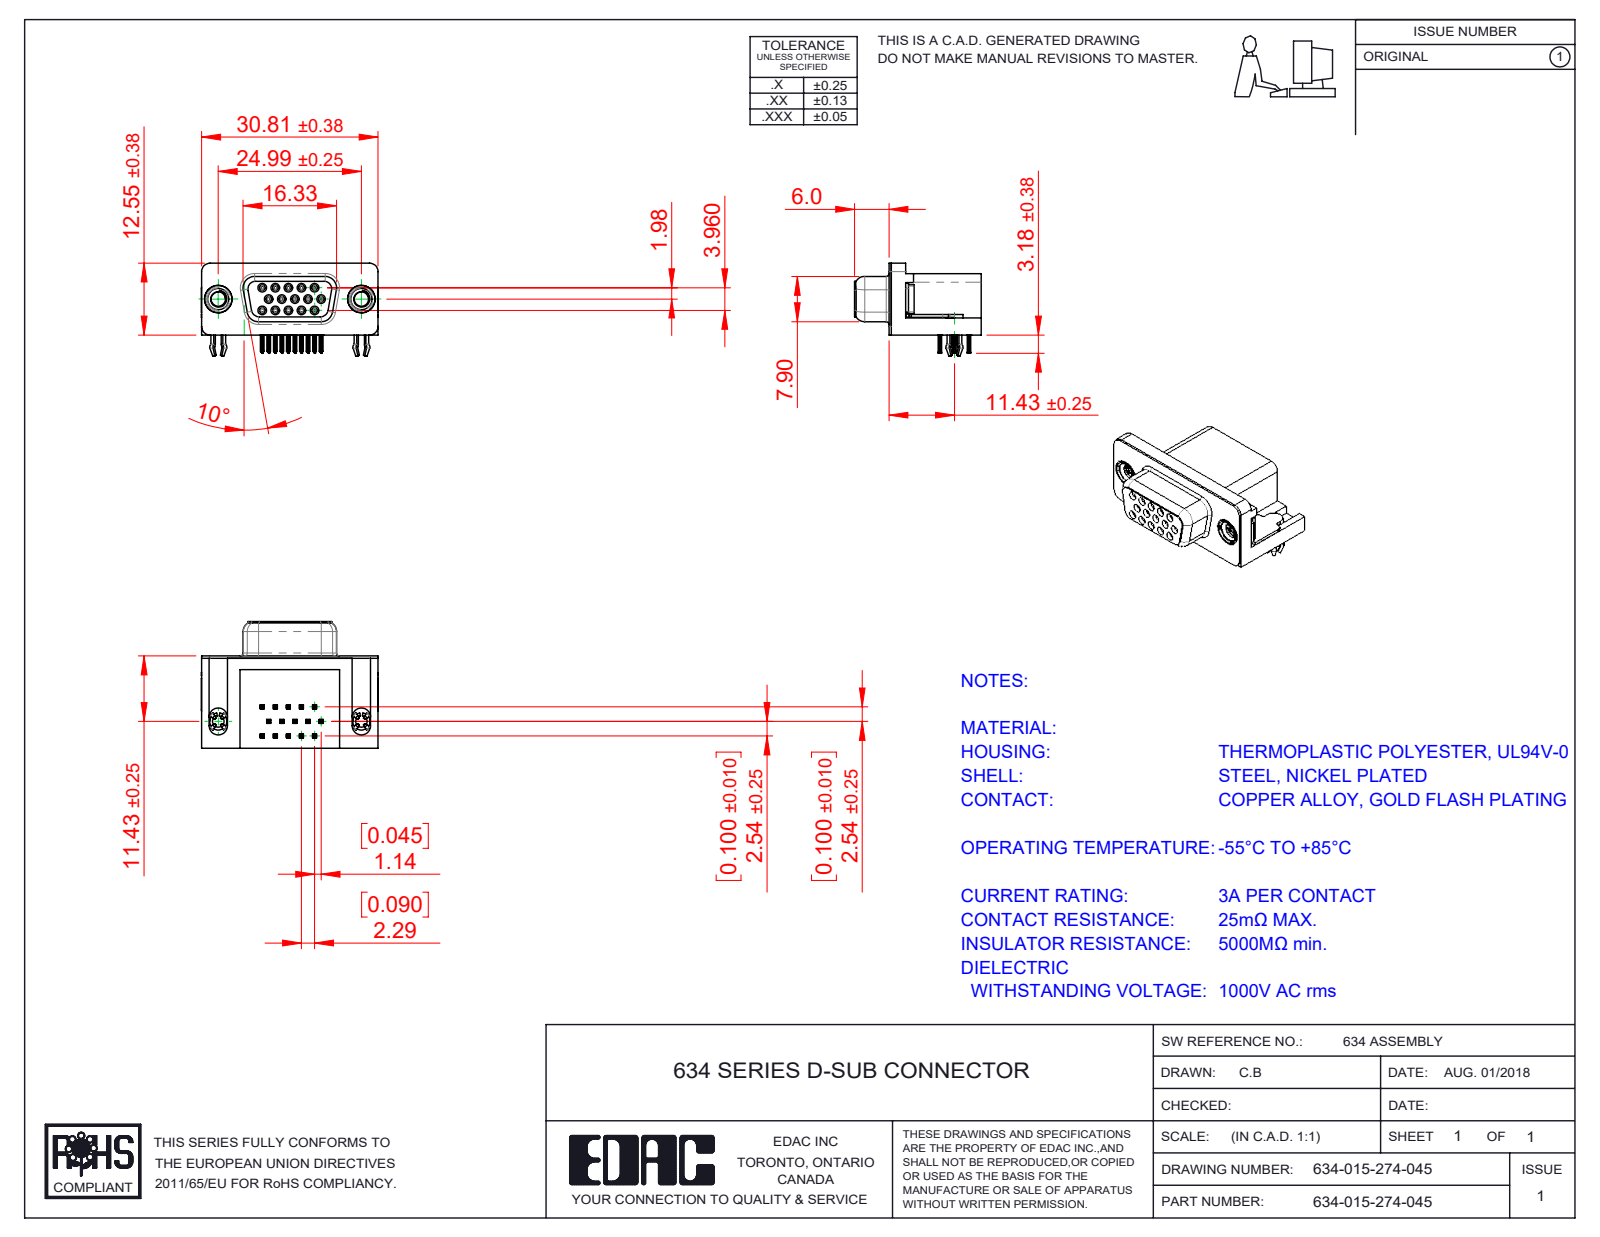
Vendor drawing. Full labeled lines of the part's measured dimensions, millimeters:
Part name (STEP PRODUCT): 634 Shell; M3 Threaded Rivet; Contact Middle; Contact Middle_Recessed (+5 more)
STEP written by: SolidWorks 2016 (CONFIG_CONTROL_DESIGN)
Units: millimetres
Bodies: 21 solids, 2541 faces (1108 planar, 609 cylindrical, 824 other)
Overall size (bounding box): 30.89 × 22.1 × 16.25
Volume: 4 557 mm³ · Surface area: 6 576 mm²
Round holes (diameter × count): ⌀0.8 ×15, ⌀0.9 ×15, ⌀2 ×2, ⌀2.5 ×2, ⌀4 ×2, ⌀4.8 ×2, ⌀5 ×2
Round bosses / shafts (diameter × count): ⌀1.2 ×15, ⌀4.9 ×2, ⌀4.75 ×2, ⌀3.9 ×2, ⌀3 ×2
Partial cylindrical surfaces — rounded edges, fillets, slot ends (radius × count): R0.1 ×120, R0.15 ×60, R0.35 ×30, R1 ×19, R0.34 ×15, R0.25 ×12, R1.35 ×8, R1.6 ×8
Main face-to-face distances: 0.4, 10.35, 15.7, 16.1, 0.35, 2.5, 2.9, 0.6, 6.4, 10.7
Hole centre spacings: 2.29, 2.28, 3.96, 4.57, 6.05, 3.97, 4.58, 6.86
